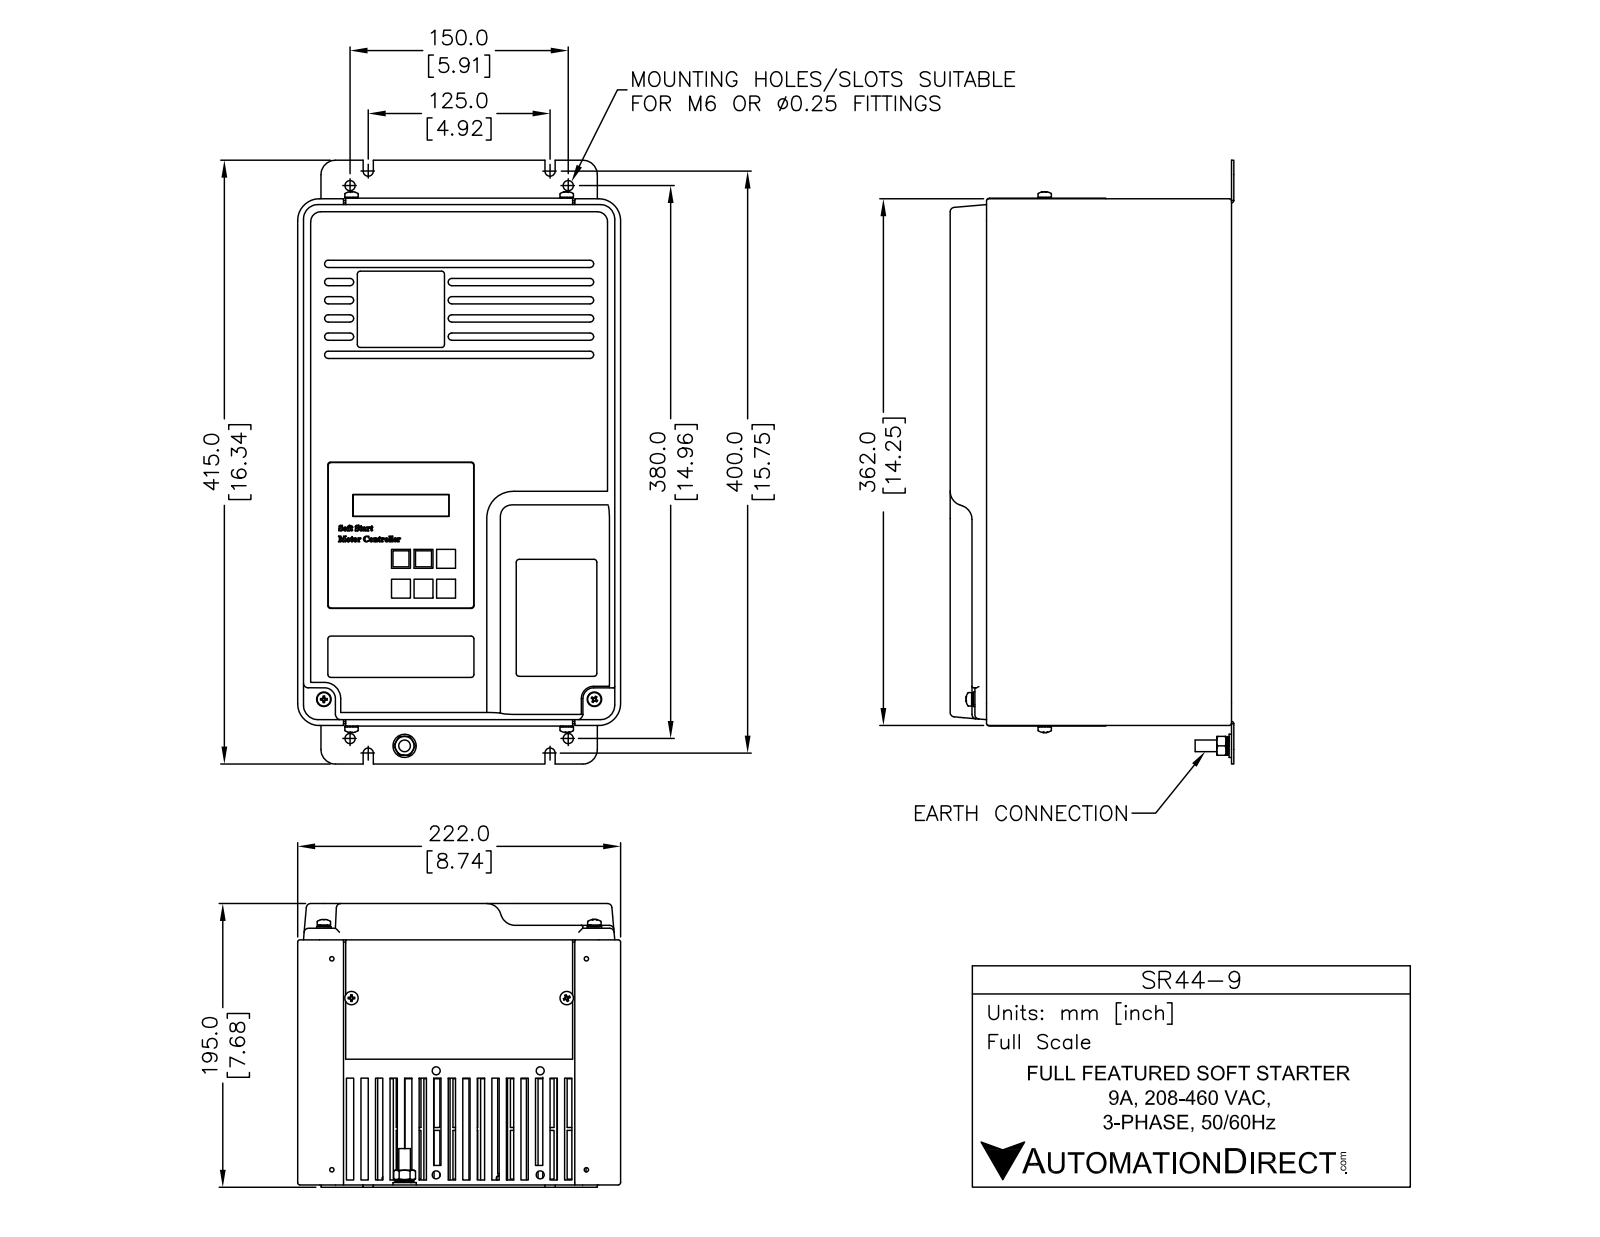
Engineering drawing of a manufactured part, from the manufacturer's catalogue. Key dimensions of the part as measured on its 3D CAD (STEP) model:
Part name (STEP PRODUCT): SR44-9
STEP written by: SolidWorks 2013 (AUTOMOTIVE_DESIGN)
Units: millimetres
Bodies: 1 solid, 768 faces (455 planar, 175 cylindrical, 138 other)
Overall size (bounding box): 415 × 222 × 194.7
Volume: 8 231 000 mm³ · Surface area: 711 054 mm²
Round holes (diameter × count): ⌀7 ×4
Round bosses / shafts (diameter × count): ⌀10 ×4, ⌀16 ×1, ⌀8 ×1
Partial cylindrical surfaces — rounded edges, fillets, slot ends (radius × count): R2.5 ×30, R2.4 ×28, R2.49 ×12, R1.5 ×11, R3 ×8, R10 ×8, R2 ×6, R3.5 ×4
Main face-to-face distances: 10.19, 20.38, 30.57, 40.76, 50.95, 61.14, 71.33, 5.9, 81.52, 216.1
Hole centre spacings: 150, 380, 408.53
